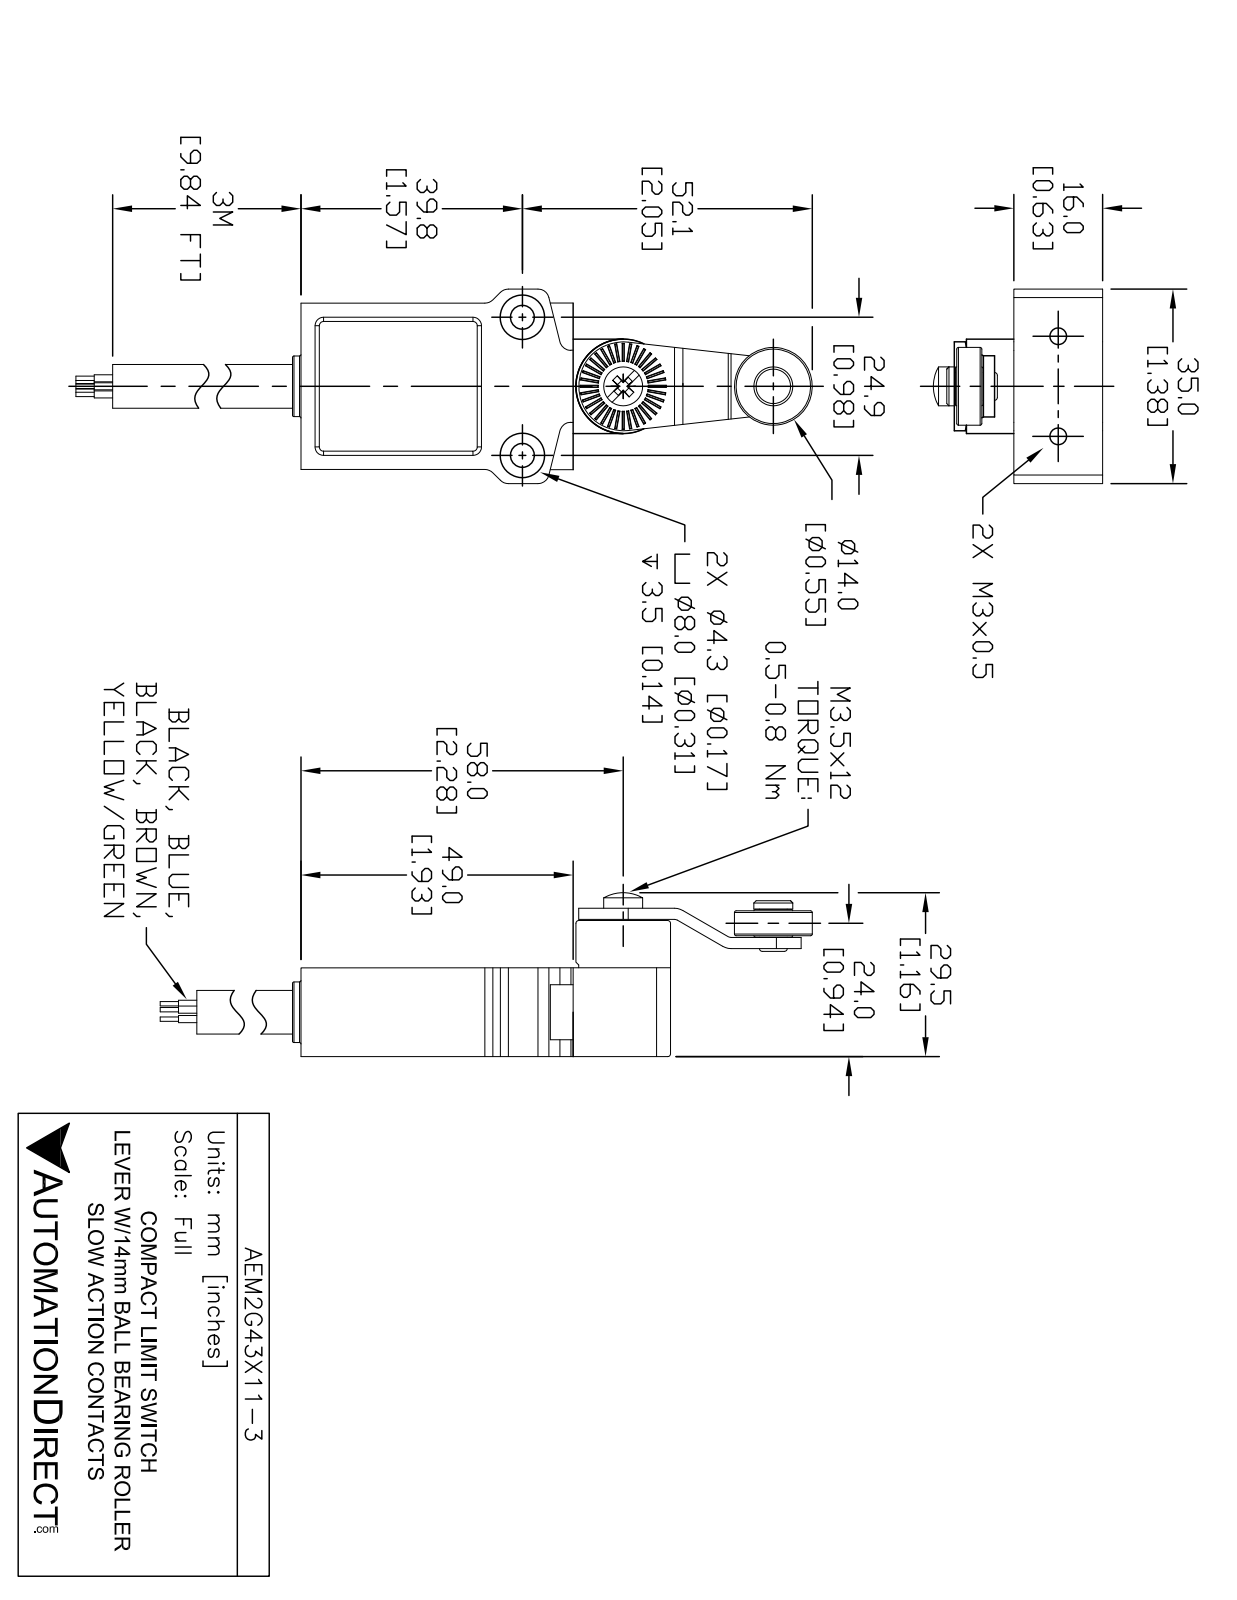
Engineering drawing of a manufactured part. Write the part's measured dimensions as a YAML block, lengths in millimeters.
part_name: "AEM2G43X11-3_Default"
step_written_by: "SolidWorks 2021 (CONFIG_CONTROL_DESIGN)"
units: millimeters
bodies: {solids: 4, faces: 308, planar: 248, cylindrical: 49, other: 11}
overall_size: [104.7, 35, 30.1]
volume: 30070
surface_area: 10680
round_holes:
  - {diameter: 3, count: 2}
  - {diameter: 4.4, count: 2}
  - {diameter: 8.2, count: 2}
  - {diameter: 5, count: 1}
round_bosses_or_shafts:
  - {diameter: 7, count: 2}
  - {diameter: 15.8, count: 1}
  - {diameter: 14, count: 1}
  - {diameter: 7.1, count: 1}
  - {diameter: 5.1, count: 1}
  - {diameter: 3.6, count: 1}
partial_cylinders:
  - {radius: 2, count: 8}
  - {radius: 1.5, count: 2}
  - {radius: 3.6, count: 1}
  - {radius: 4.9, count: 1}
  - {radius: 6.5, count: 1}
  - {radius: 8, count: 1}
face_to_face_distances: [16, 30, 49, 9, 2, 25, 3.1, 7.1, 22.9, 12]
hole_center_spacings: [21.9, 19, 25]
